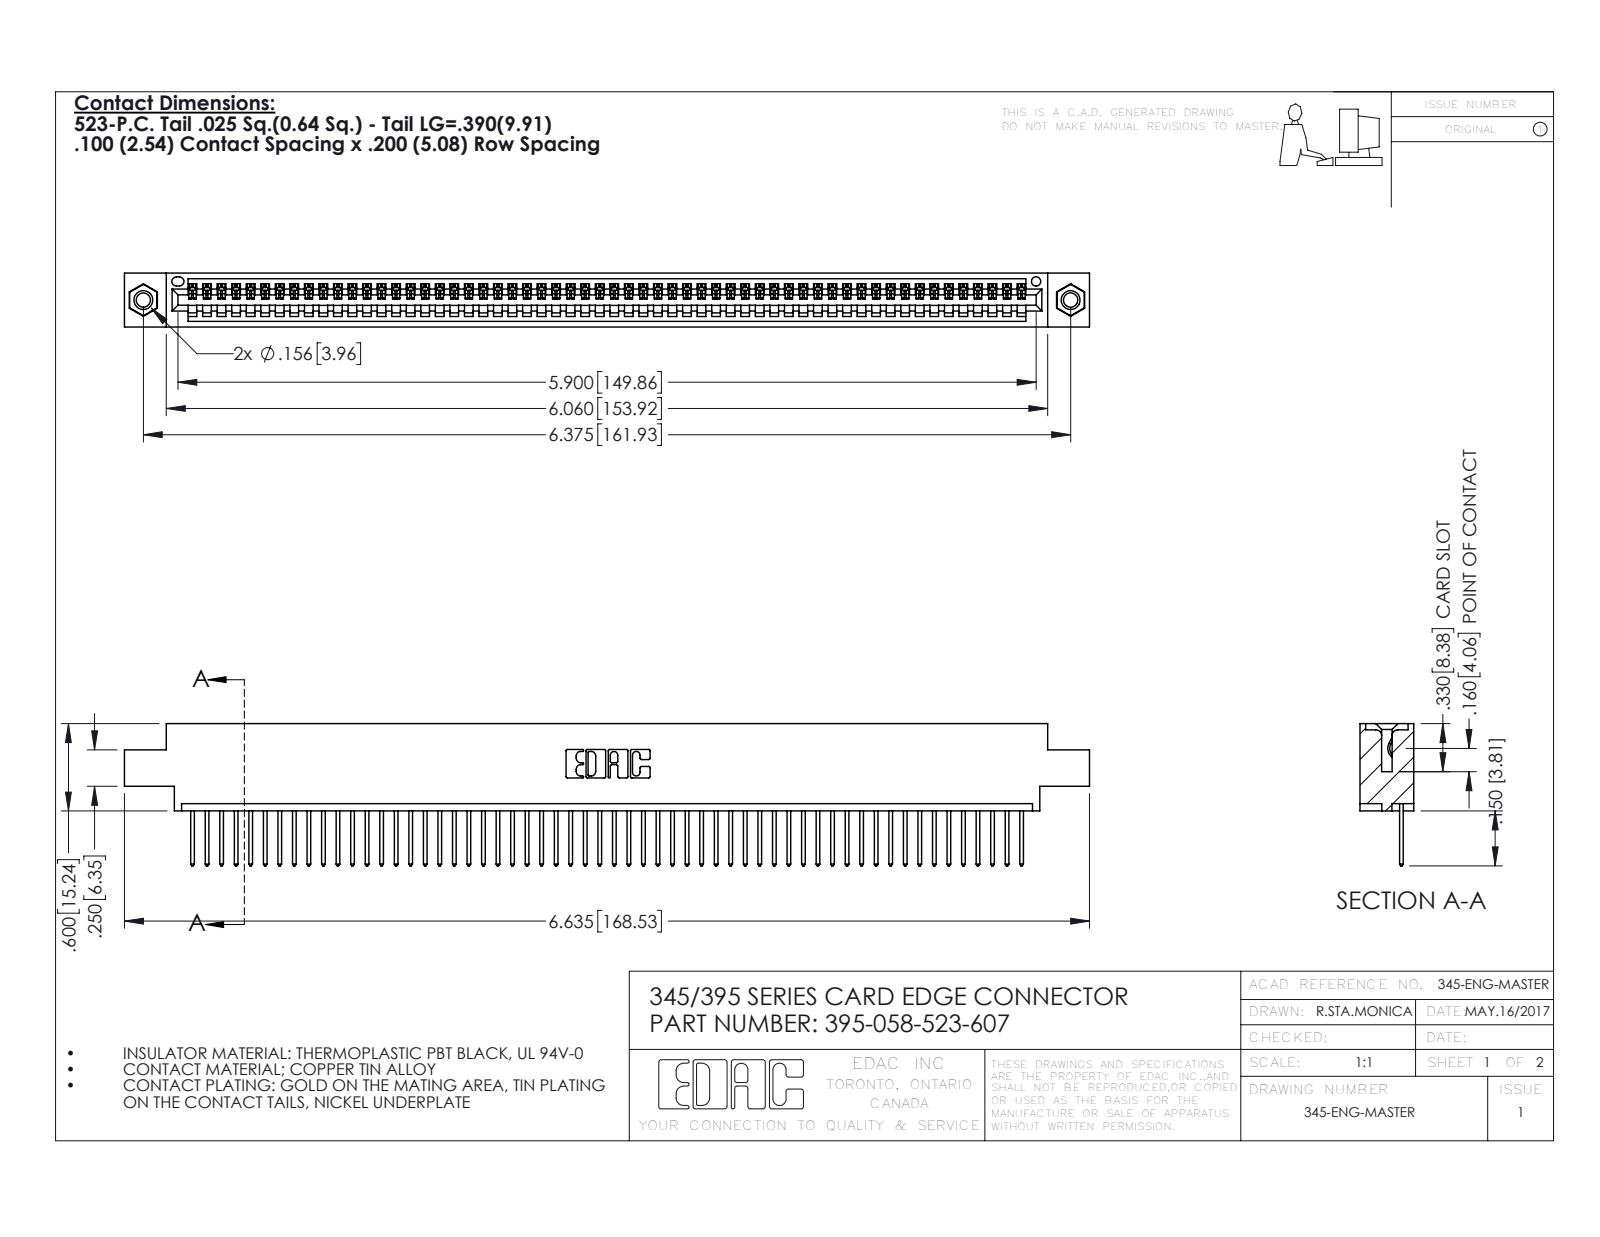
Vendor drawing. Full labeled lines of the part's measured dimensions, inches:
Part name (STEP PRODUCT): 345-292-001_345-293-123; 395-058-523-607; 345-250-001_345-250-005-103; 345 Part_0.170 Offset - 0.156 Dia-TI
STEP written by: SolidWorks 2016 (CONFIG_CONTROL_DESIGN)
Units: inches
Bodies: 61 solids, 3554 faces (2436 planar, 1102 cylindrical, 16 other)
Overall size (bounding box): 6.635 × 0.977 × 0.37
Volume: 0.976 in³ · Surface area: 33.62 in²
Round holes (diameter × count): ⌀0.098 ×2, ⌀0.125 ×2, ⌀0.156 ×2, ⌀0.064 ×1
Round bosses / shafts (diameter × count): ⌀0.155 ×2
Partial cylindrical surfaces — rounded edges, fillets, slot ends (radius × count): R0.006 ×116, R0.01 ×116, R0.01 ×22, R0.007 ×6, R0.031 ×6, R0.026 ×3, R0.031 ×2, R0.04 ×2
Main face-to-face distances: 0.072, 0.298, 0.37, 0.098, 0.272, 0.025, 0.2, 0.225, 0.175, 0.149
Hole centre spacings: 0.27, 6.139, 6.375
